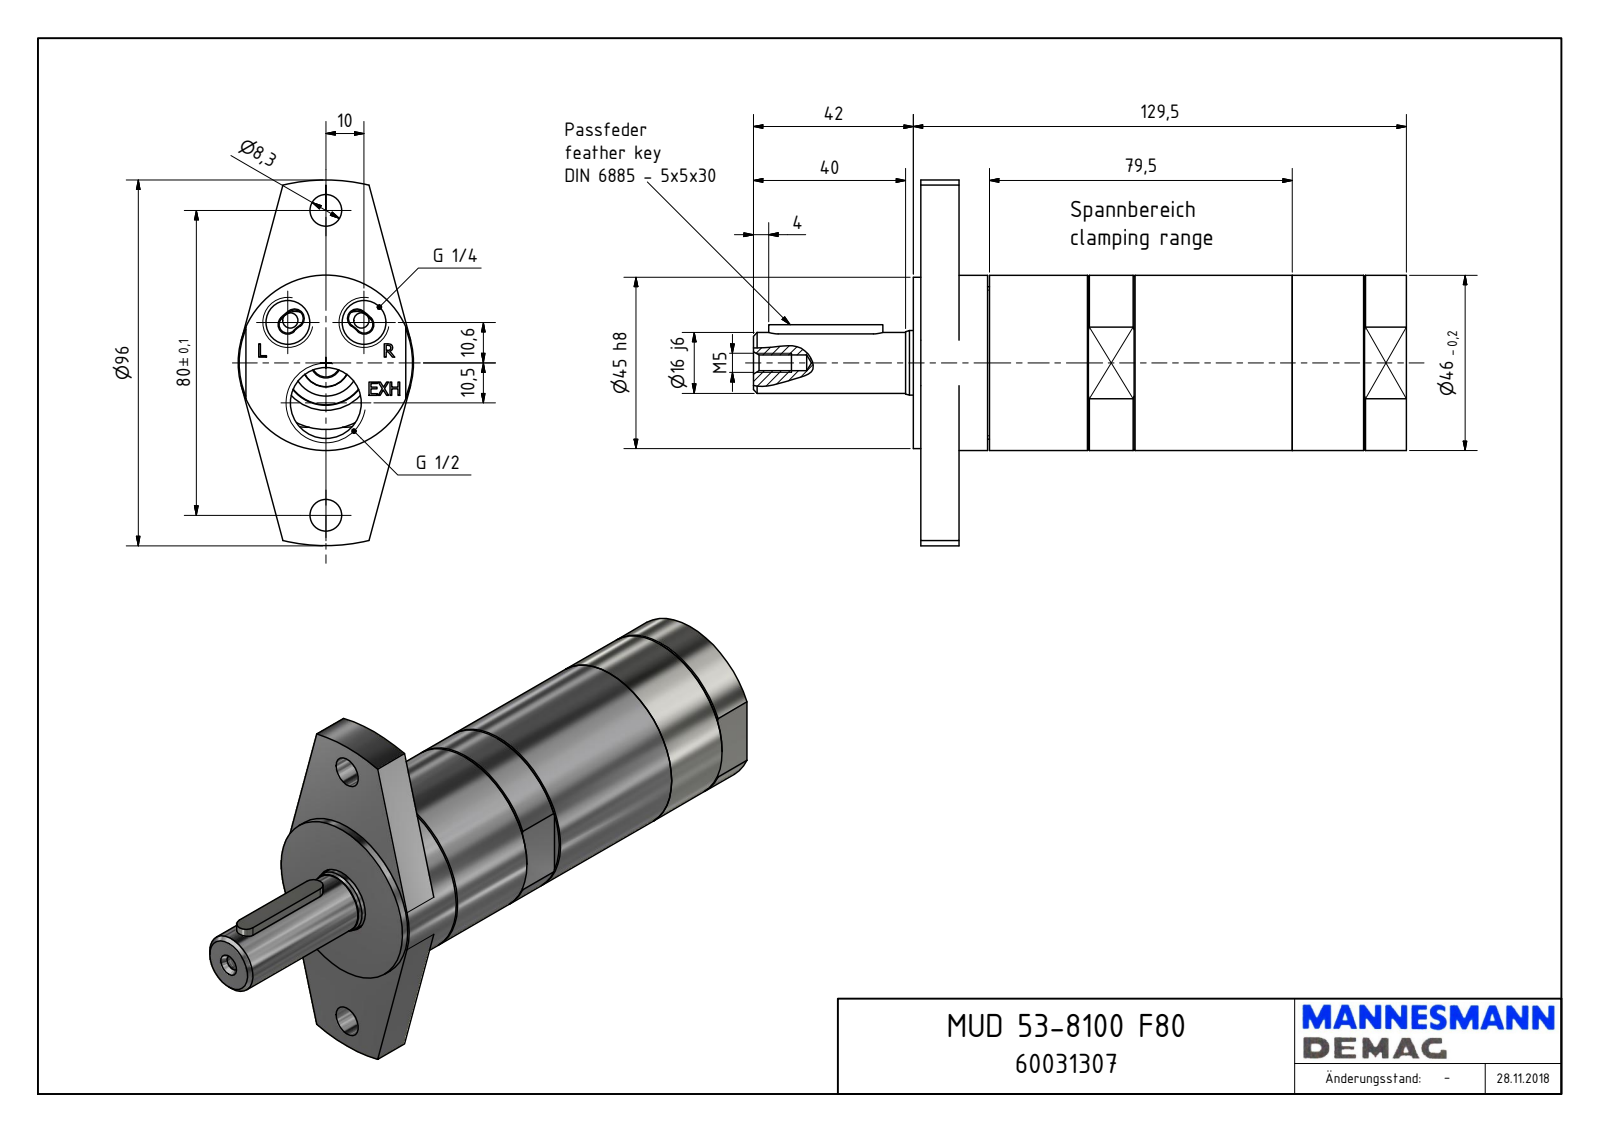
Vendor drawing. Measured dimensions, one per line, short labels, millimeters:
name: MUD 53-8100 F80_60031307
written by: Autodesk Inventor 2018 (AUTOMOTIVE_DESIGN)
unit: mm
bodies: 1 solid, 171 faces (101 planar, 40 cylindrical, 30 other)
size: 171.5 × 96 × 46
volume: 232 844 mm³; area: 33 064 mm²
holes: 2× ⌀8.3, 2× ⌀11.45, 1× ⌀4.13, 1× ⌀17.5, 1× ⌀18.63, 1× ⌀21.5, 1× ⌀23
bosses: 1× ⌀46, 1× ⌀45, 1× ⌀40, 1× ⌀33.26, 1× ⌀19.56, 1× ⌀16.95, 1× ⌀16
rounds: 6× R2.5, 2× R5, 1× R16.75, 1× R19, 1× R48
face distances: 10, 12, 2, 129.5, 127.5, 117.5, 42, 8, 109.5, 46
hole spacings: 14.57, 23.35, 31.05, 40, 51.58, 10.5, 20, 29.5
